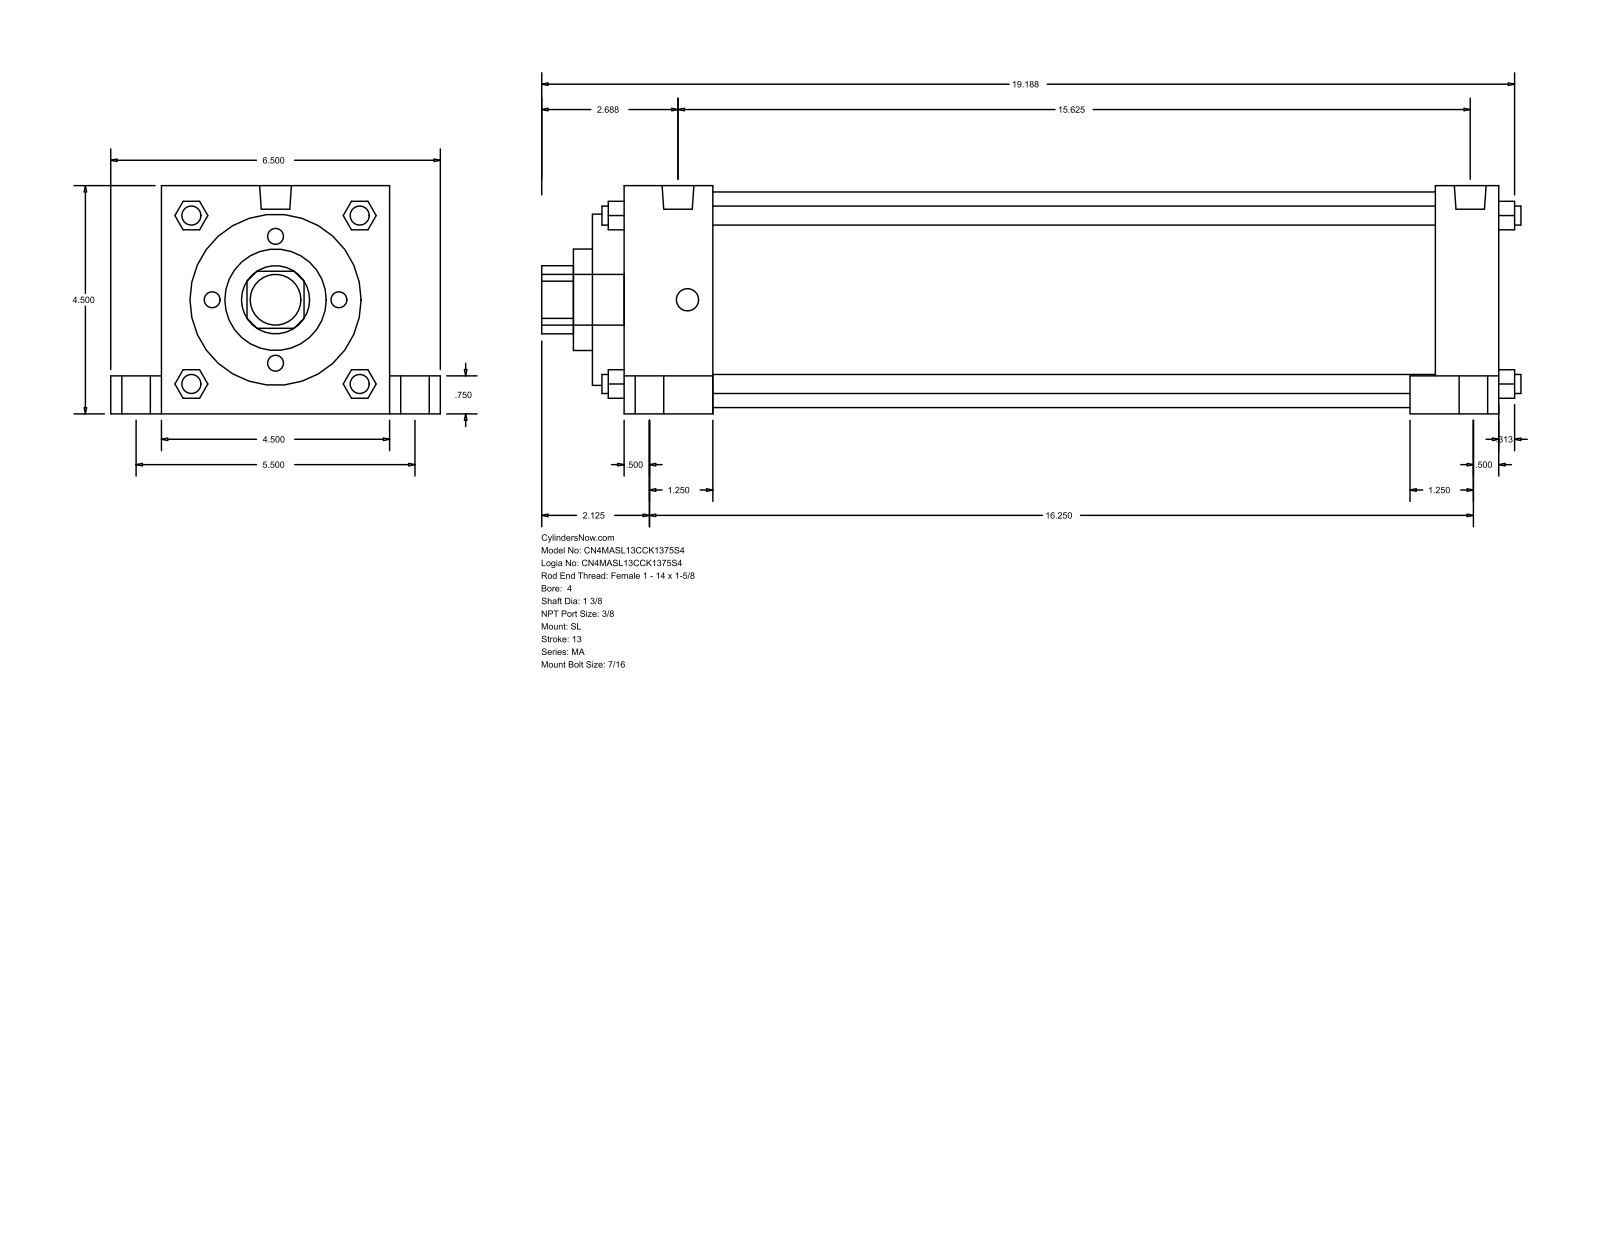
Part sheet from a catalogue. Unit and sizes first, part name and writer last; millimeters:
Units: millimetres
Overall size (bounding box): 490.54 × 165.1 × 114.3
Round holes (diameter × count): ⌀34.92 ×1, ⌀50.8 ×1, ⌀85.72 ×1, ⌀107.95 ×1
Round bosses / shafts (diameter × count): ⌀20.64 ×4, ⌀14.29 ×4, ⌀11.11 ×4, ⌀9.53 ×4, ⌀15.93 ×2, ⌀25.4 ×1
Partial cylindrical surfaces — rounded edges, fillets, slot ends (radius × count): R17.06 ×1
Main face-to-face distances: 114.3, 438.16, 15.87, 454.03, 60.32, 44.45, 393.71, 422.28, 406.41, 361.96
Bodies: 0 solids, 150 faces (113 planar, 37 cylindrical, 0 other)
Part name (STEP PRODUCT): MA_SL__0400_1.375
STEP written by: GSSL Pune (CONFIG_CONTROL_DESIGN)
